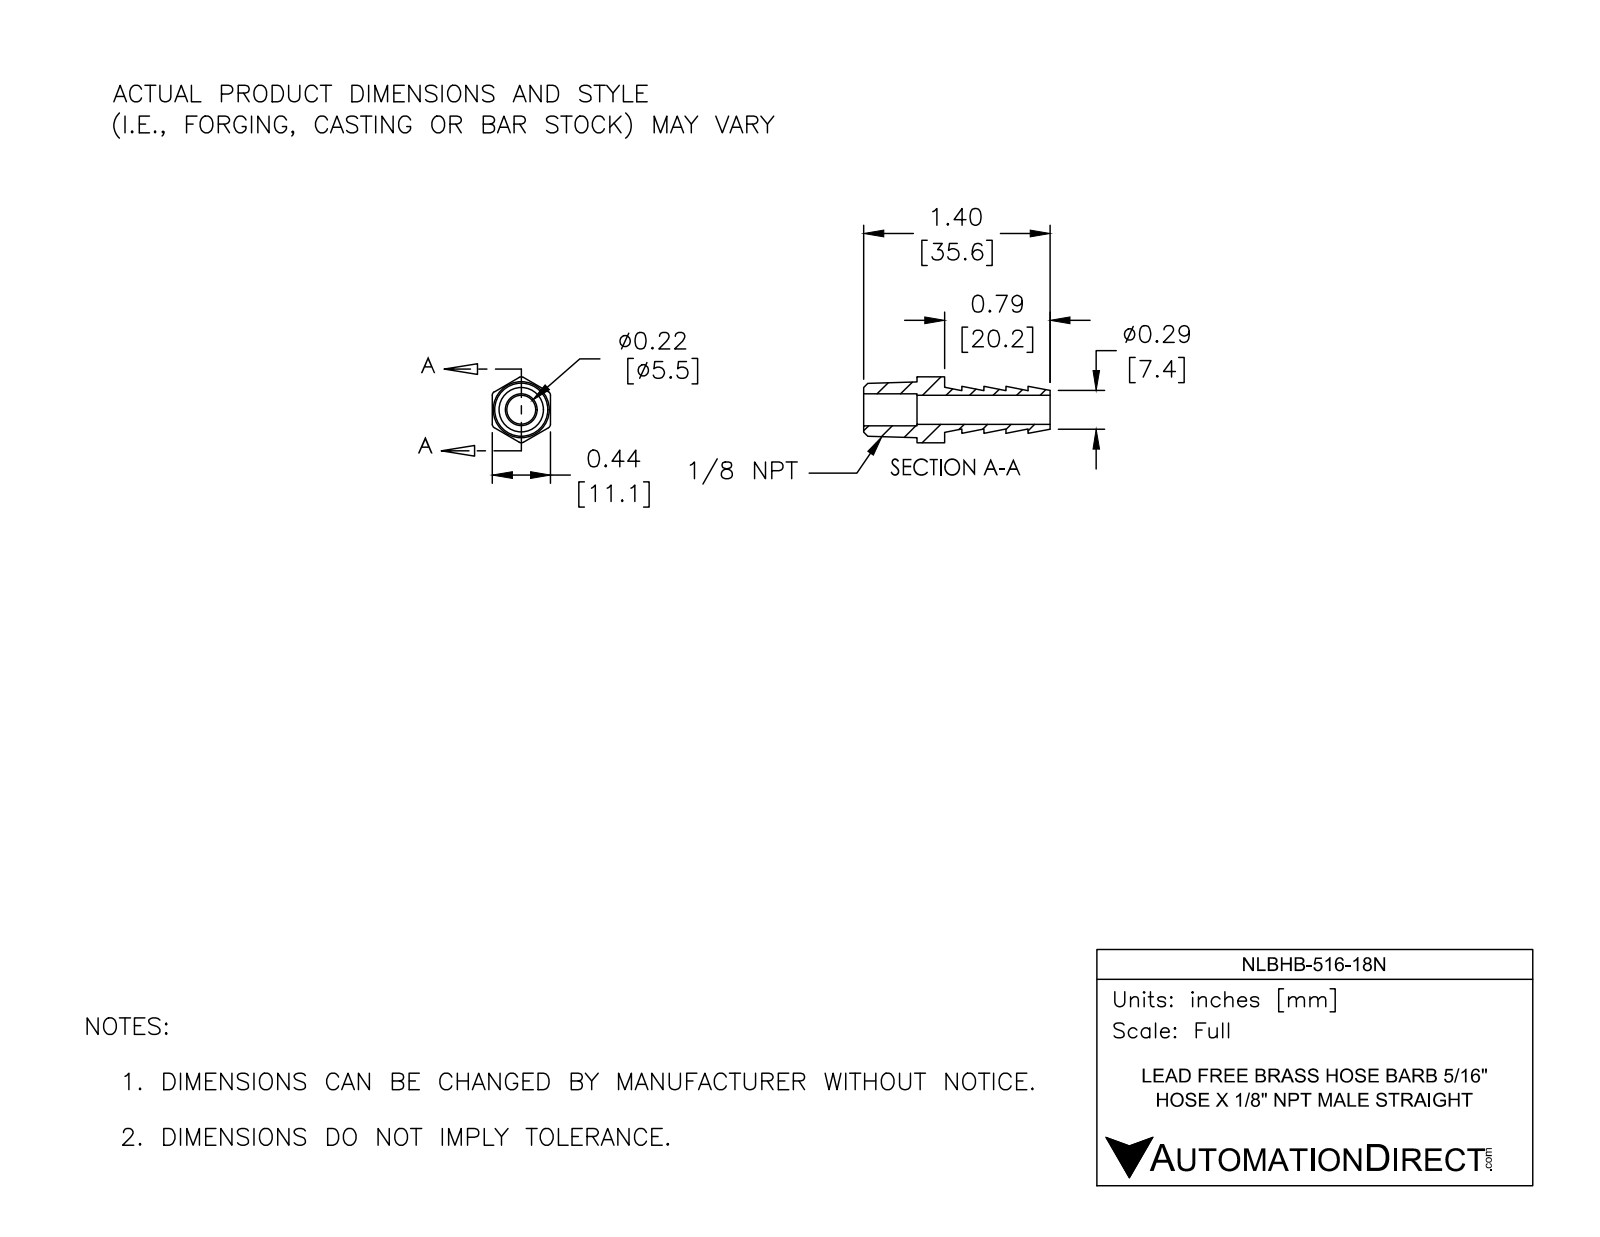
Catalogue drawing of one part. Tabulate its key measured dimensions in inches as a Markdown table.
| quantity | value |
| --- | --- |
| part name | NLBHB-516-18N |
| STEP written by | SolidWorks 2017 (AUTOMOTIVE_DESIGN) |
| units | inches |
| bodies | 1 solid, 39 faces (15 planar, 10 cylindrical, 14 other) |
| overall size | 1.402 × 0.496 × 0.438 |
| volume | 0.095 in³ |
| surface area | 2.952 in² |
| round holes (diameter × count) | 0.218 × 1, 0.24 × 1 |
| partial cylindrical surfaces (radius × count) | 0.03 × 6 |
| main face-to-face distances | 0.438, 0.166, 0.332, 0.498, 0.608, 0.208, 0.4, 0.166, 0.628, 0.836 |
